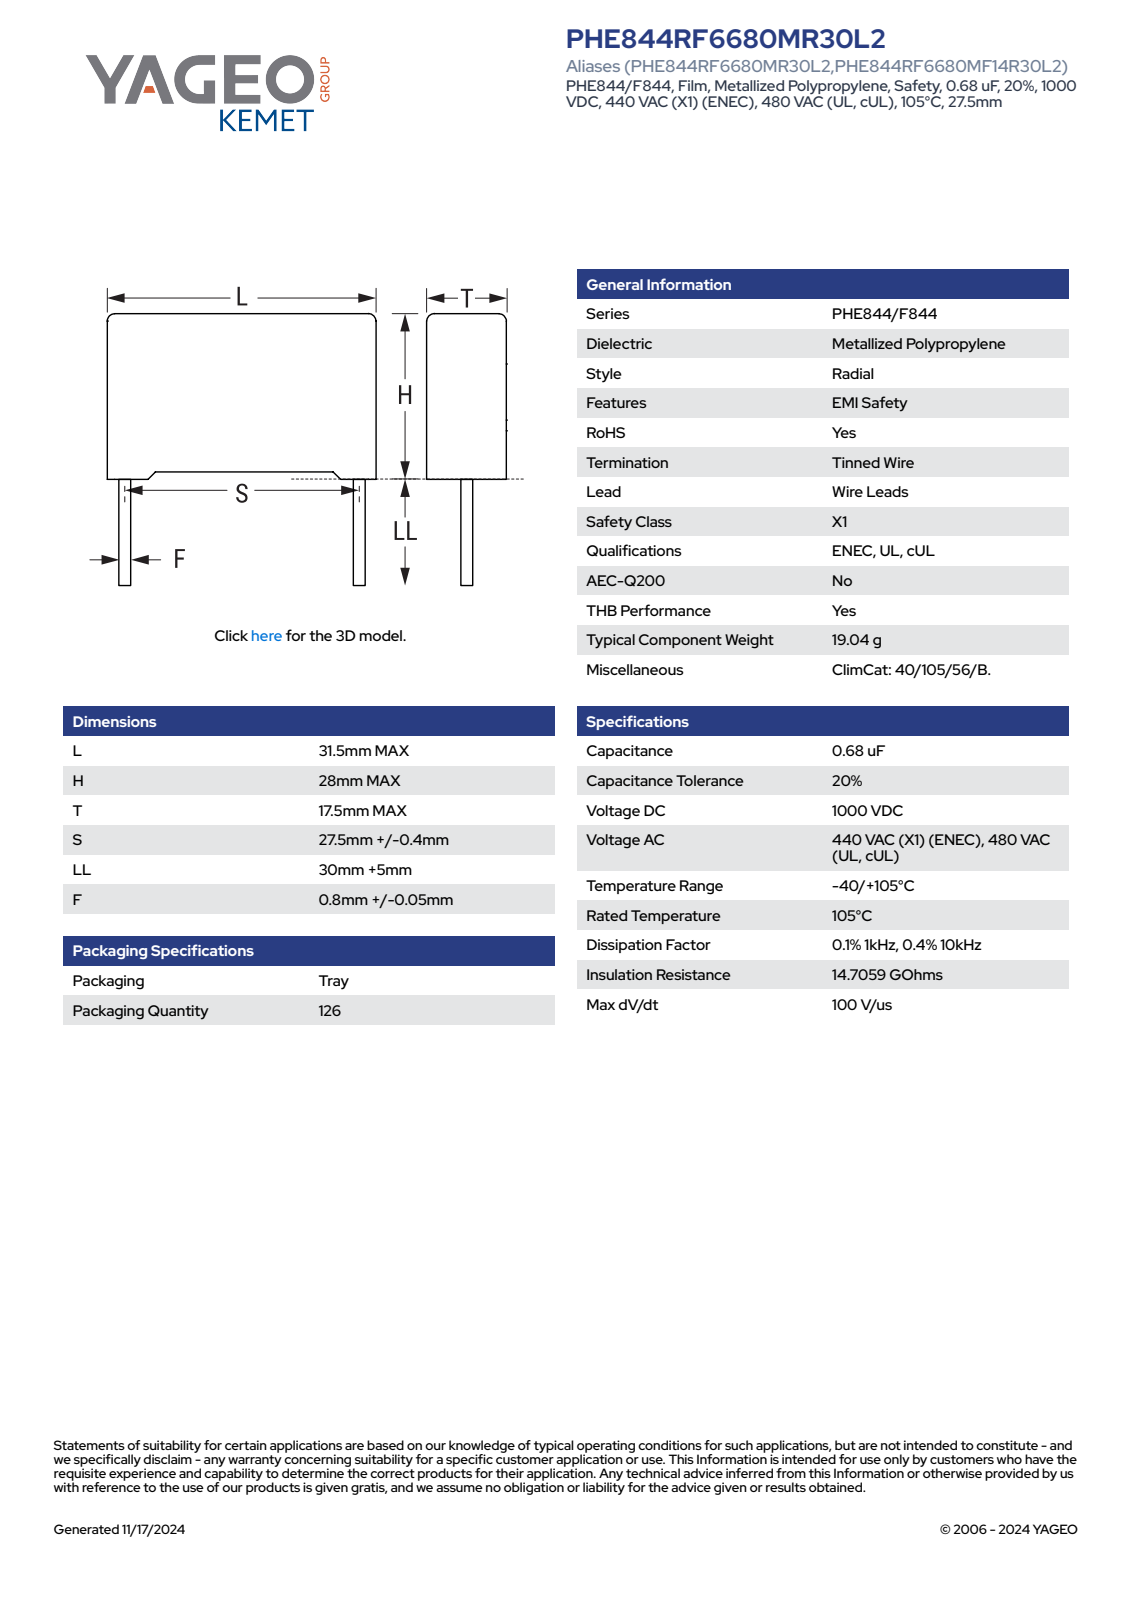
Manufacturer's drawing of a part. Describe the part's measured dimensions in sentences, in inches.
The part is named "CFR_RB2_31.5X28X17.5_L31.5H28T17.5S27.5LL35F0.85". Its 3-D file was written by "SolidWorks 2021 (AUTOMOTIVE_DESIGN)". It is 4 solids with 85 faces: 77 planar, 8 cylindrical and 0 other. Overall it measures 2.48 by 1.24 by 0.689 inches. Its volume is 0.916 cubic inches and its surface area 6.326 square inches. Round bosses or shafts: 2 of diameter 0.033. Partial cylindrical surfaces (rounded edges, fillets, slot ends): 4 of radius 0.02. The main face-to-face distances are 0.689, 1.24, 1.064, 1.073, 0.038, 0.03, 1.102, 0.041, 1.199, 0.689.
